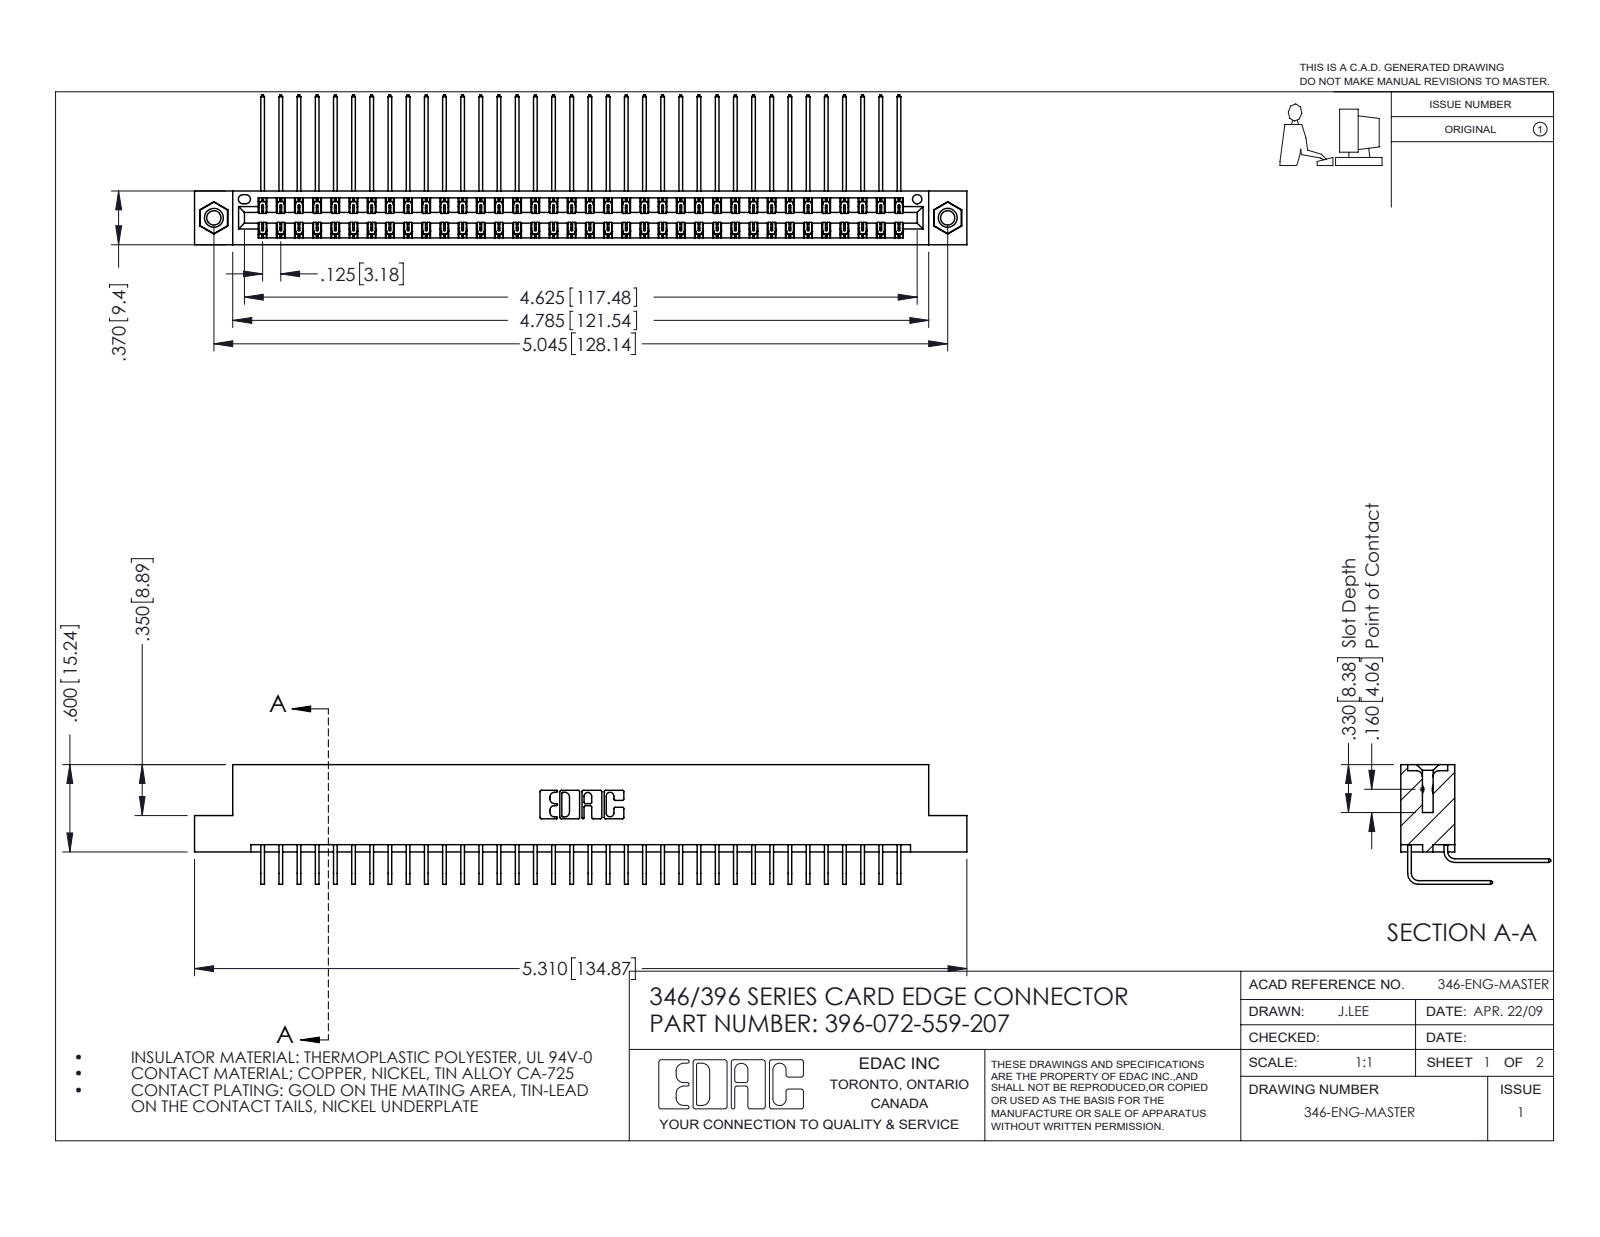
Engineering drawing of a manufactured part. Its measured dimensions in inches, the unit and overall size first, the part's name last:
Units: inches
Overall size (bounding box): 5.31 × 1.03 × 0.823
Round holes (diameter × count): ⌀0.098 ×2, ⌀0.125 ×2, ⌀0.156 ×2, ⌀0.064 ×1
Round bosses / shafts (diameter × count): ⌀0.155 ×2
Partial cylindrical surfaces — rounded edges, fillets, slot ends (radius × count): R0.006 ×108, R0.01 ×22, R0.007 ×6, R0.031 ×6, R0.026 ×3, R0.014 ×2, R0.022 ×2, R0.024 ×2
Main face-to-face distances: 0.048, 0.322, 0.025, 0.37, 0.25, 0.072, 0.298, 0.275, 0.148, 0.222
Hole centre spacings: 0.246, 4.836, 5.045
Volume: 0.824 in³ · Surface area: 31.77 in²
Bodies: 75 solids, 4070 faces (2772 planar, 1282 cylindrical, 16 other)
Part name (STEP PRODUCT): 346 Part_Flush Mounting Lugs - 0.156 Dia-TI; 345-292-001_559 Tail - 2; 345-250-001_345-250-005-103; 345-292-001_558 559 Tail - 1 (+1 more)
STEP written by: SolidWorks 2016 (CONFIG_CONTROL_DESIGN)
